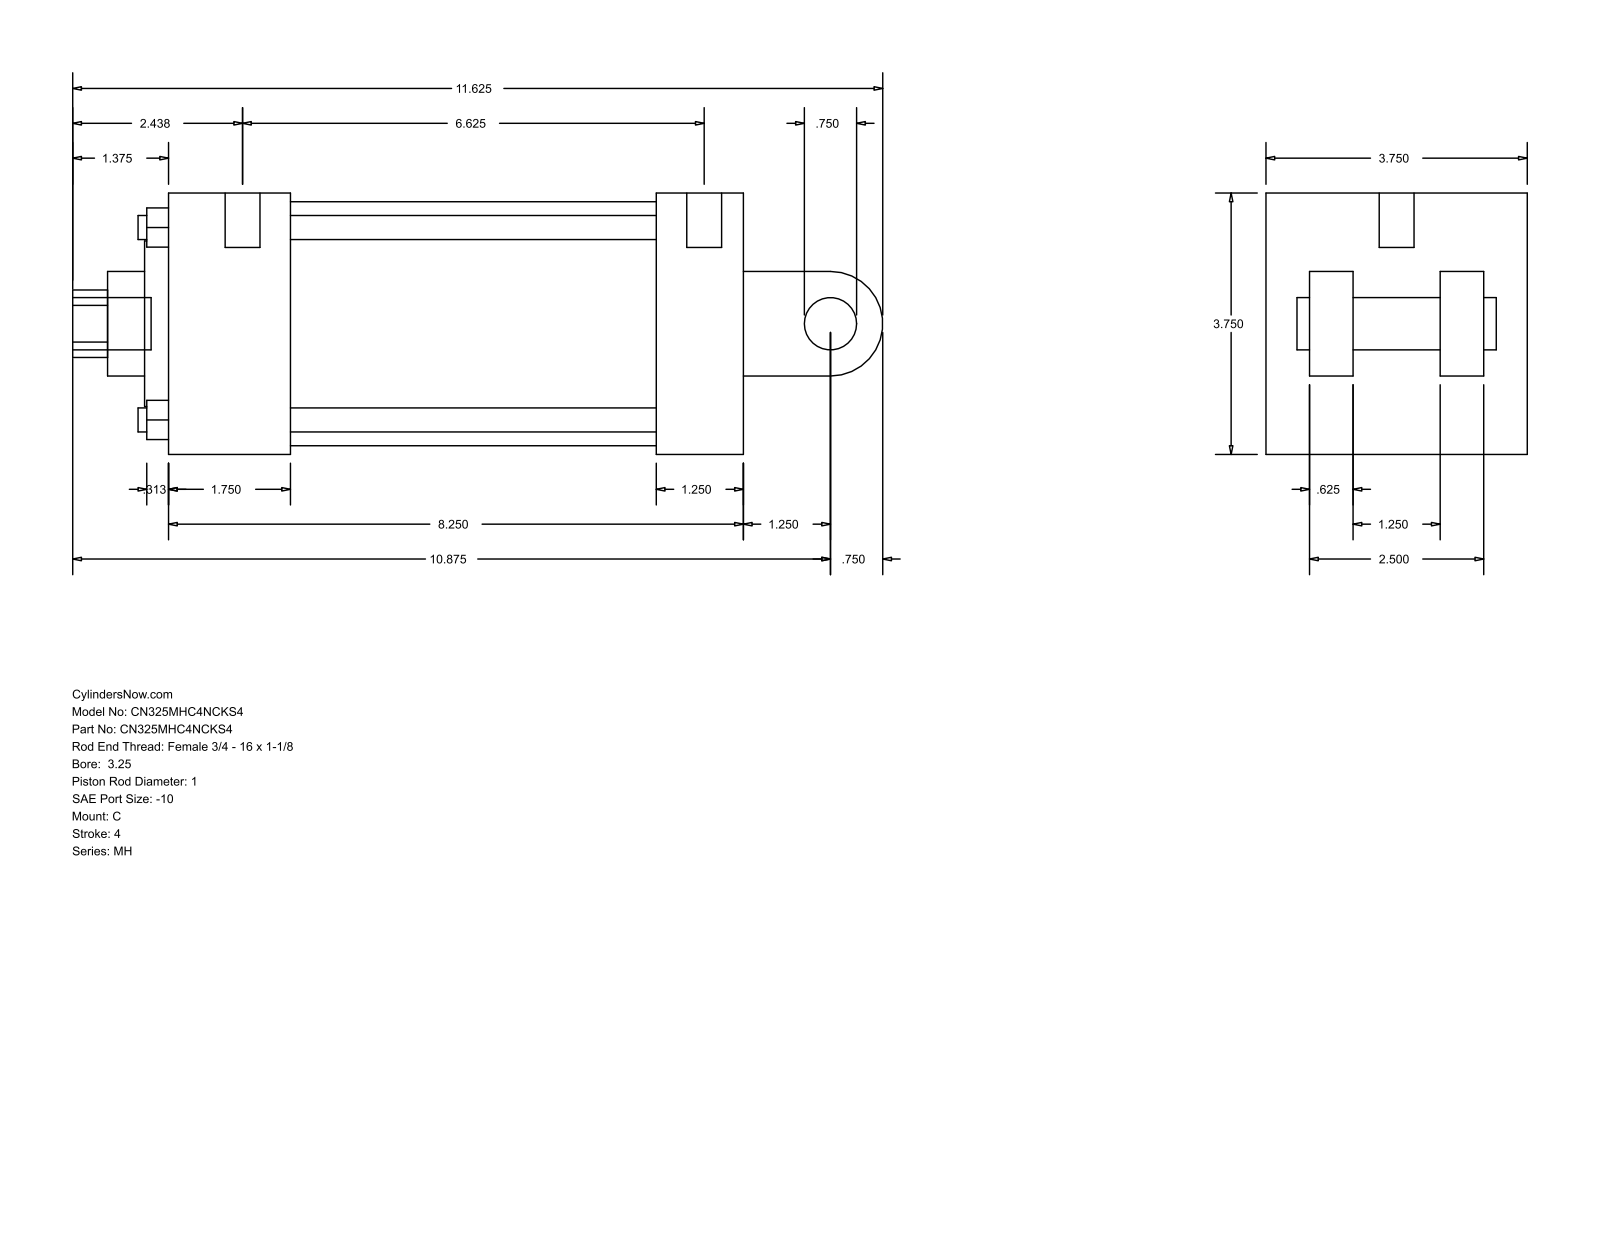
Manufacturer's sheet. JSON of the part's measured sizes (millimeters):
{"part_name": "MH_C__0325_1", "step_written_by": "GSSL Pune (CONFIG_CONTROL_DESIGN)", "units": "millimeters", "bodies": {"solids": 0, "faces": 101, "planar": 71, "cylindrical": 30, "other": 0}, "overall_size": [295.27, 95.25, 95.25], "round_holes": [[8.76, 4], [5.56, 2], [12.7, 1], [25.4, 1], [38.1, 1], [60.33, 1], [88.9, 1]], "round_bosses_or_shafts": [[19.05, 2], [5.56, 2], [12.7, 1]], "partial_cylinders_radius": [[12.29, 1], [19.05, 1]], "face_to_face_distances": [95.24, 15.87, 209.55, 63.5, 79.37, 31.74, 47.63, 44.46, 177.8, 133.34], "hole_center_spacings": [49.57, 70.1, 99.14, 4.76]}
